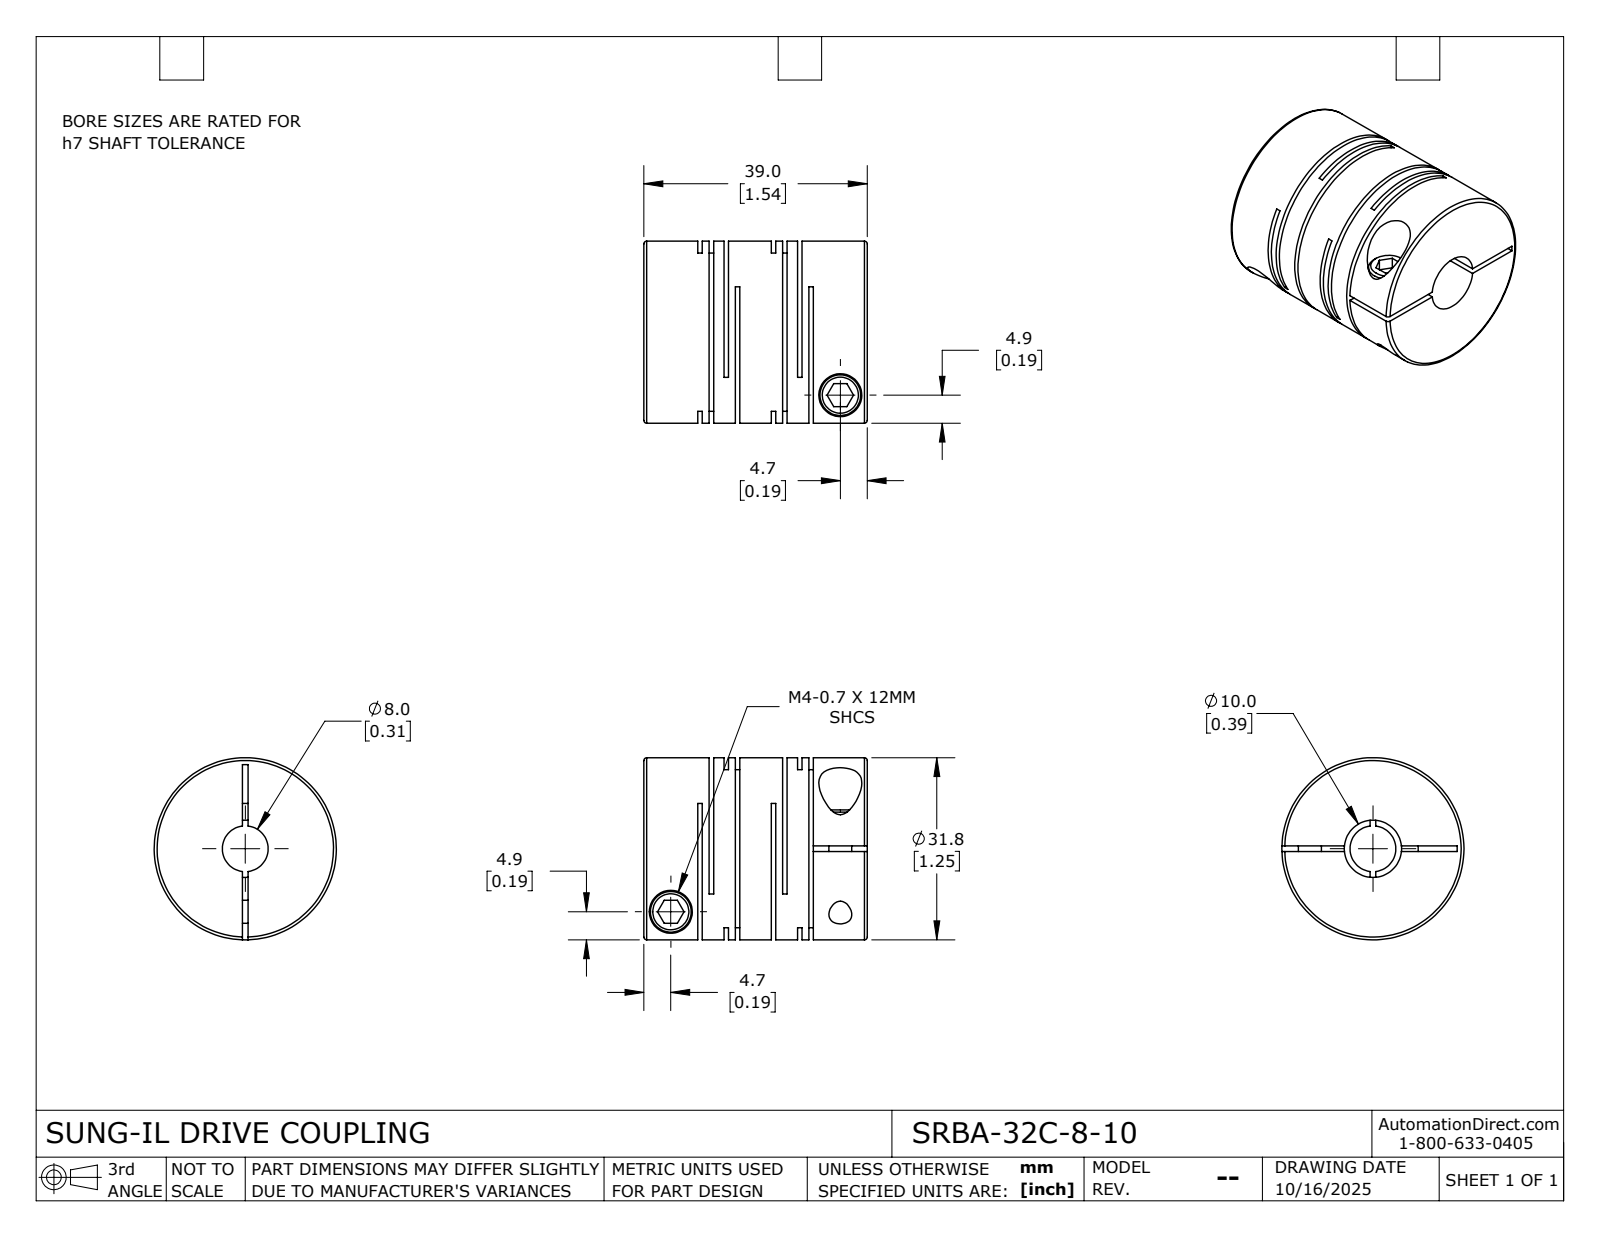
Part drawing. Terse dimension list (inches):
name: SRBA-32C-8-10
written by: SolidWorks 2024 (CONFIG_CONTROL_DESIGN)
unit: in
bodies: 1 solid, 115 faces (60 planar, 42 cylindrical, 13 other)
size: 1.535 × 1.252 × 1.252
volume: 1.445 in³; area: 25.17 in²
holes: 2× ⌀0.157, 2× ⌀0.295, 1× ⌀0.315, 1× ⌀0.394
bosses: 2× ⌀0.28, 1× ⌀1.252
face distances: 0.031, 0.506, 0.078, 0.18, 0.474, 0.046, 0.428, 0.149, 0.325, 0.102
